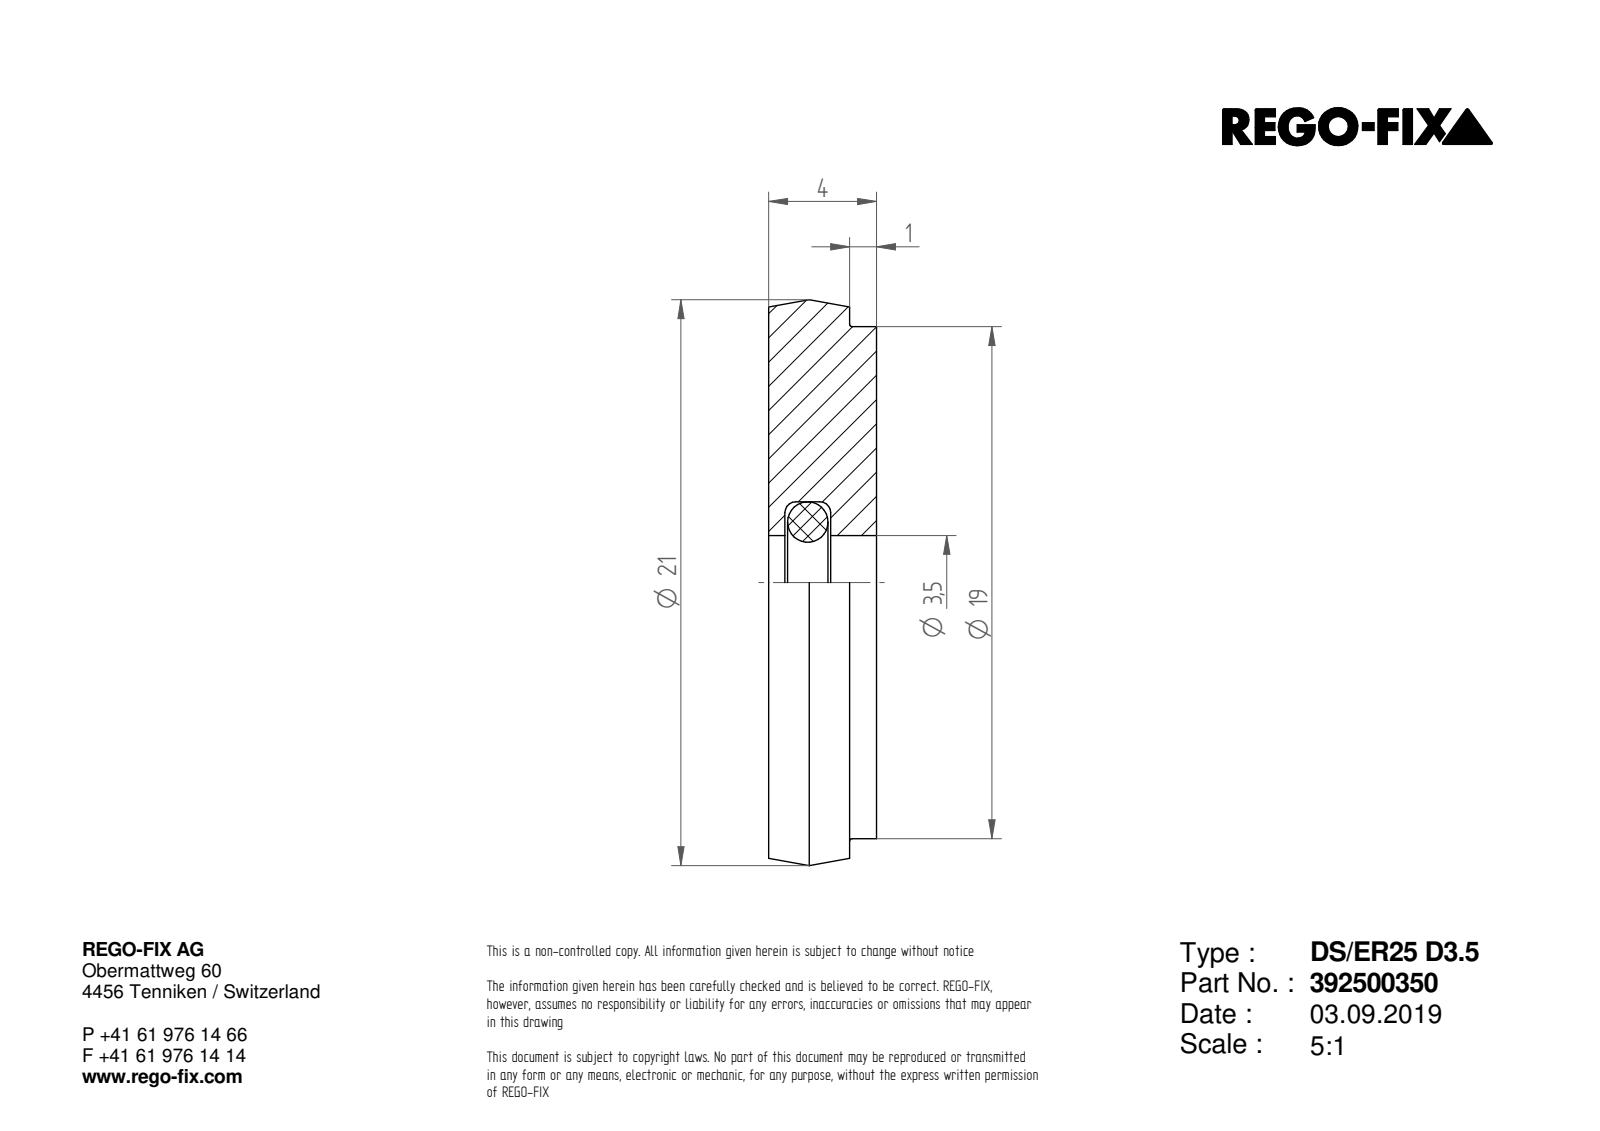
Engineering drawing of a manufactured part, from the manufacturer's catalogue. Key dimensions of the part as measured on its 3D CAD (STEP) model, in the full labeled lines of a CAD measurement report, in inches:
Part name (STEP PRODUCT): NOCUT
STEP written by: SIEMENS PLM Software Solid Edge ST10 (AUTOMOTIVE_DESIGN)
Units: inches
Bodies: 1 solid, 7 faces (3 planar, 3 cylindrical, 1 other)
Overall size (bounding box): 0.827 × 0.827 × 0.157
Volume: 0.078 in³ · Surface area: 1.51 in²
Round holes (diameter × count): ⌀0.138 ×1
Round bosses / shafts (diameter × count): ⌀0.827 ×1, ⌀0.748 ×1
Main face-to-face distances: 0.157, 0.039, 0.118
